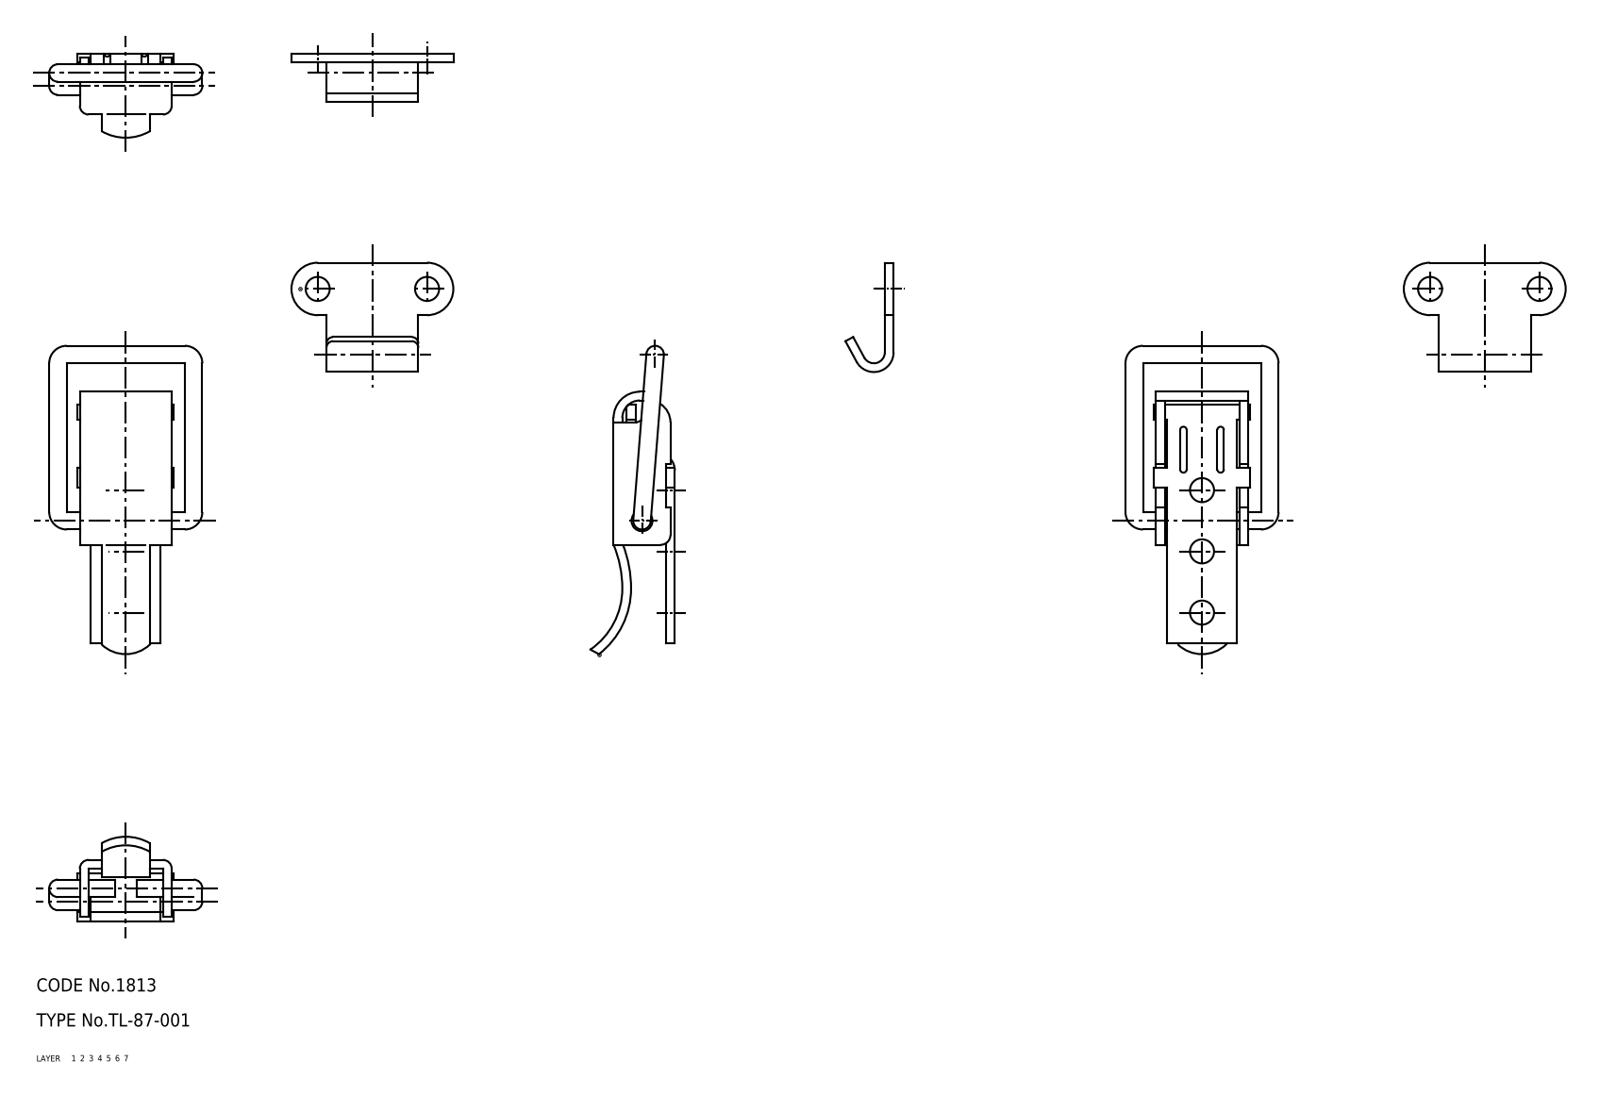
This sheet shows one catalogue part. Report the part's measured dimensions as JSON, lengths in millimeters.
{"part_name": "lever; keeper; base; arm (+1 more)", "step_written_by": "CADfix (AUTOMOTIVE_DESIGN)", "units": "millimeters", "bodies": {"solids": 4, "faces": 175, "planar": 0, "cylindrical": 0, "other": 175}, "overall_size": [89.5, 37, 19.3], "volume_mm3": 8543, "surface_area_mm2": 9897}
